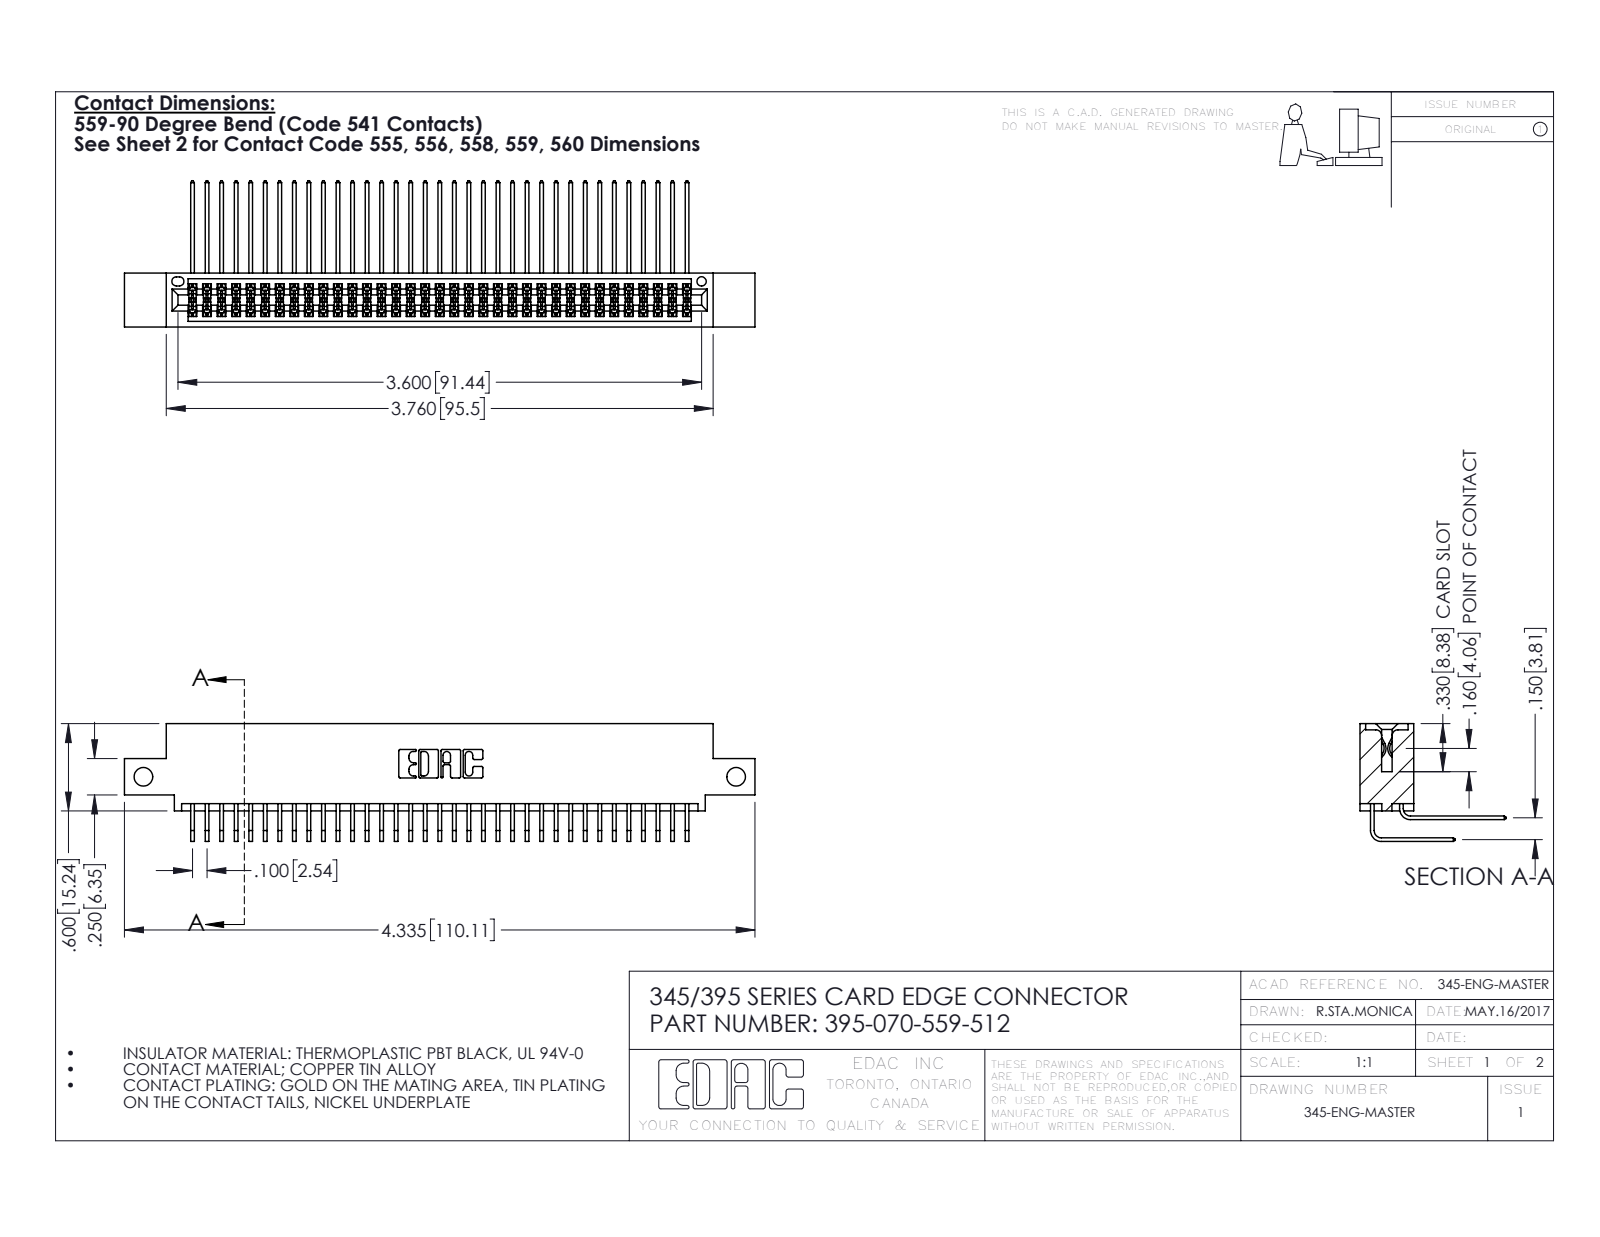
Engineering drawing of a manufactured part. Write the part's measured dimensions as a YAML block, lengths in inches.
part_name: "395-070-559-512; 345-292-001_558 559 Tail - 1; 345-292-001_559 Tail - 2; 345 Part_0.110 Offset - Side Mount"
step_written_by: "SolidWorks 2016 (CONFIG_CONTROL_DESIGN)"
units: inches
bodies: {solids: 71, faces: 3770, planar: 2534, cylindrical: 1236, other: 0}
overall_size: [4.335, 1.005, 0.809]
volume: 0.664
surface_area: 27.58
round_holes:
  - {diameter: 0.128, count: 2}
  - {diameter: 0.064, count: 1}
partial_cylinders:
  - {radius: 0.006, count: 105}
  - {radius: 0.01, count: 22}
  - {radius: 0.007, count: 6}
  - {radius: 0.031, count: 6}
  - {radius: 0.026, count: 3}
  - {radius: 0.014, count: 2}
  - {radius: 0.019, count: 2}
  - {radius: 0.022, count: 2}
face_to_face_distances: [0.072, 0.298, 0.37, 0.2, 0.098, 0.272, 0.025, 0.225, 0.175, 0.15]
hole_center_spacings: [4.075]
